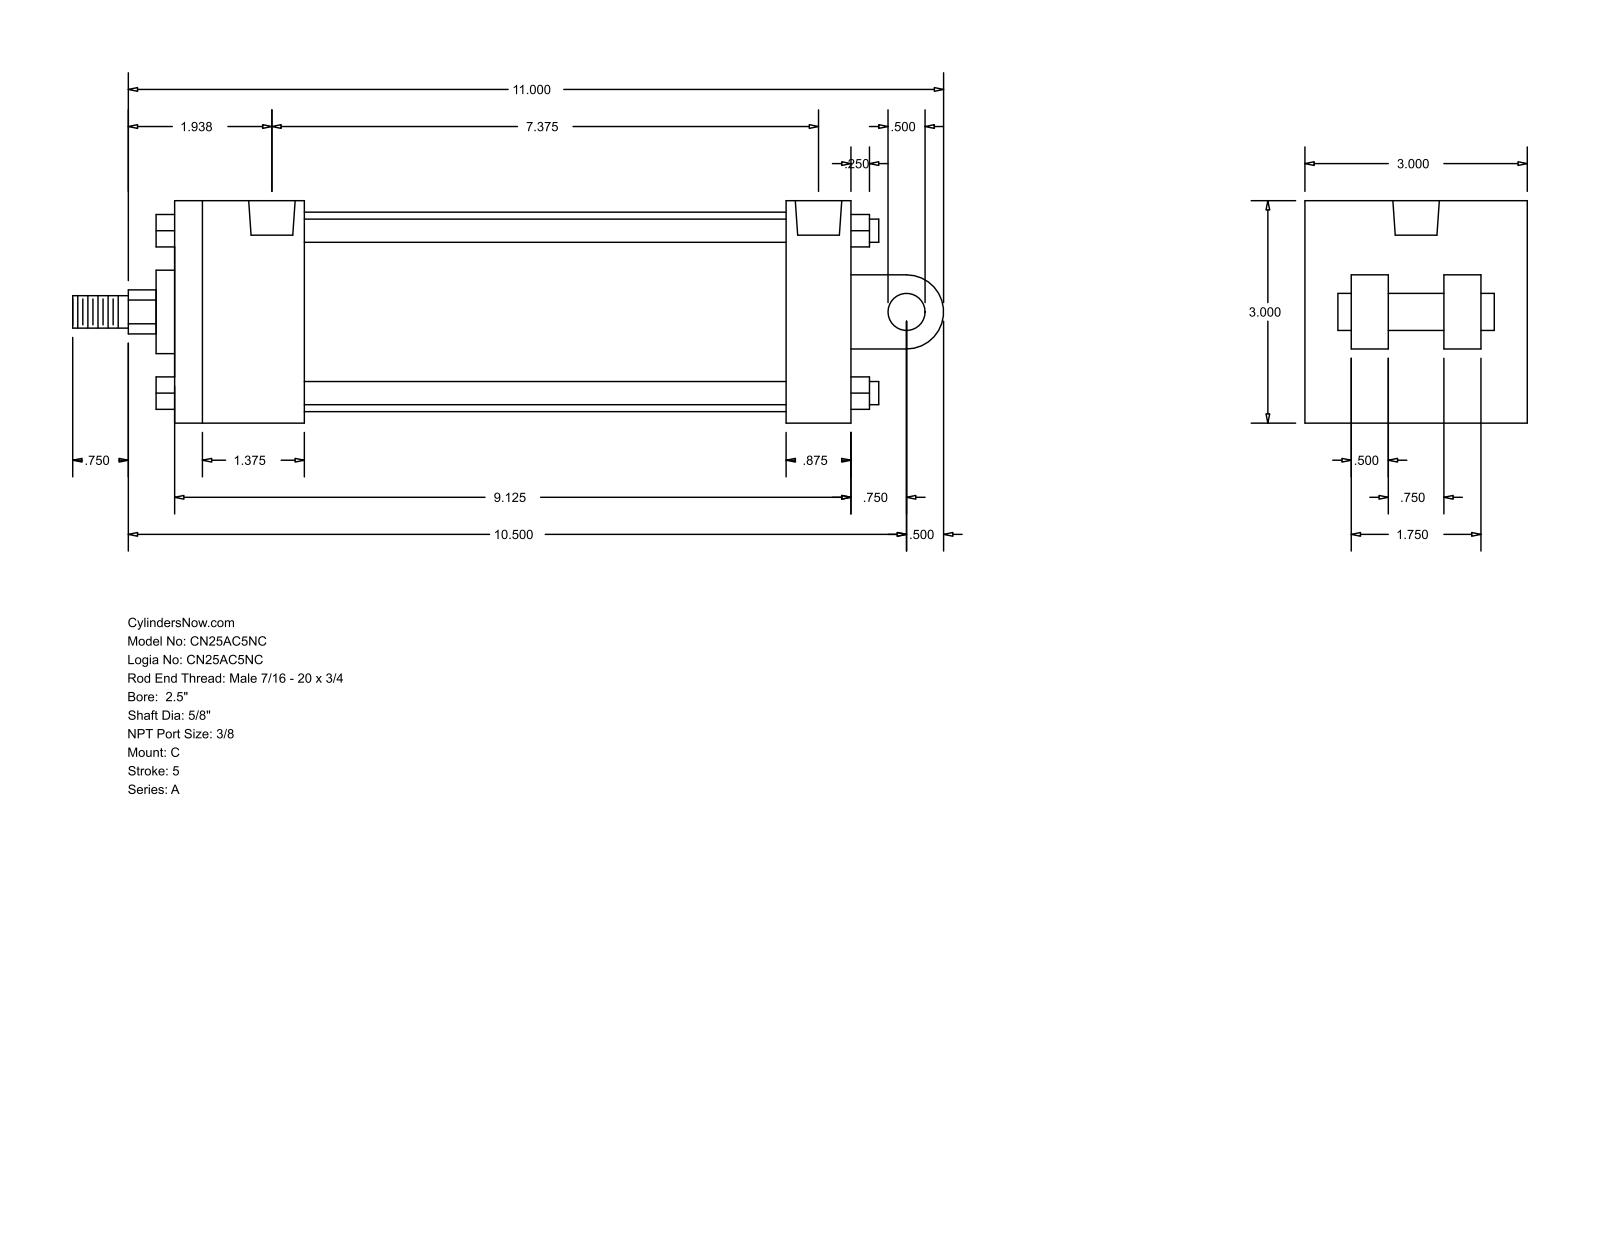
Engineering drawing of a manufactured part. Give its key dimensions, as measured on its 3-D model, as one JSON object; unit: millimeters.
{"part_name": "A_C__0250_0.625", "step_written_by": "GSSL Pune (CONFIG_CONTROL_DESIGN)", "units": "millimeters", "bodies": {"solids": 0, "faces": 135, "planar": 102, "cylindrical": 33, "other": 0}, "overall_size": [298.45, 76.2, 76.2], "round_holes": [[5.56, 4], [15.93, 2]], "round_bosses_or_shafts": [[7.94, 4], [68.33, 1], [28.57, 1], [15.88, 1], [12.7, 1], [11.11, 1]], "partial_cylinders_radius": [[7.54, 1], [12.7, 1]], "face_to_face_distances": [76.2, 231.77, 44.45, 209.55, 165.1, 187.32, 22.22, 50.8, 12.7, 25.4], "hole_center_spacings": [2.38, 189.71, 192.09, 187.33]}
